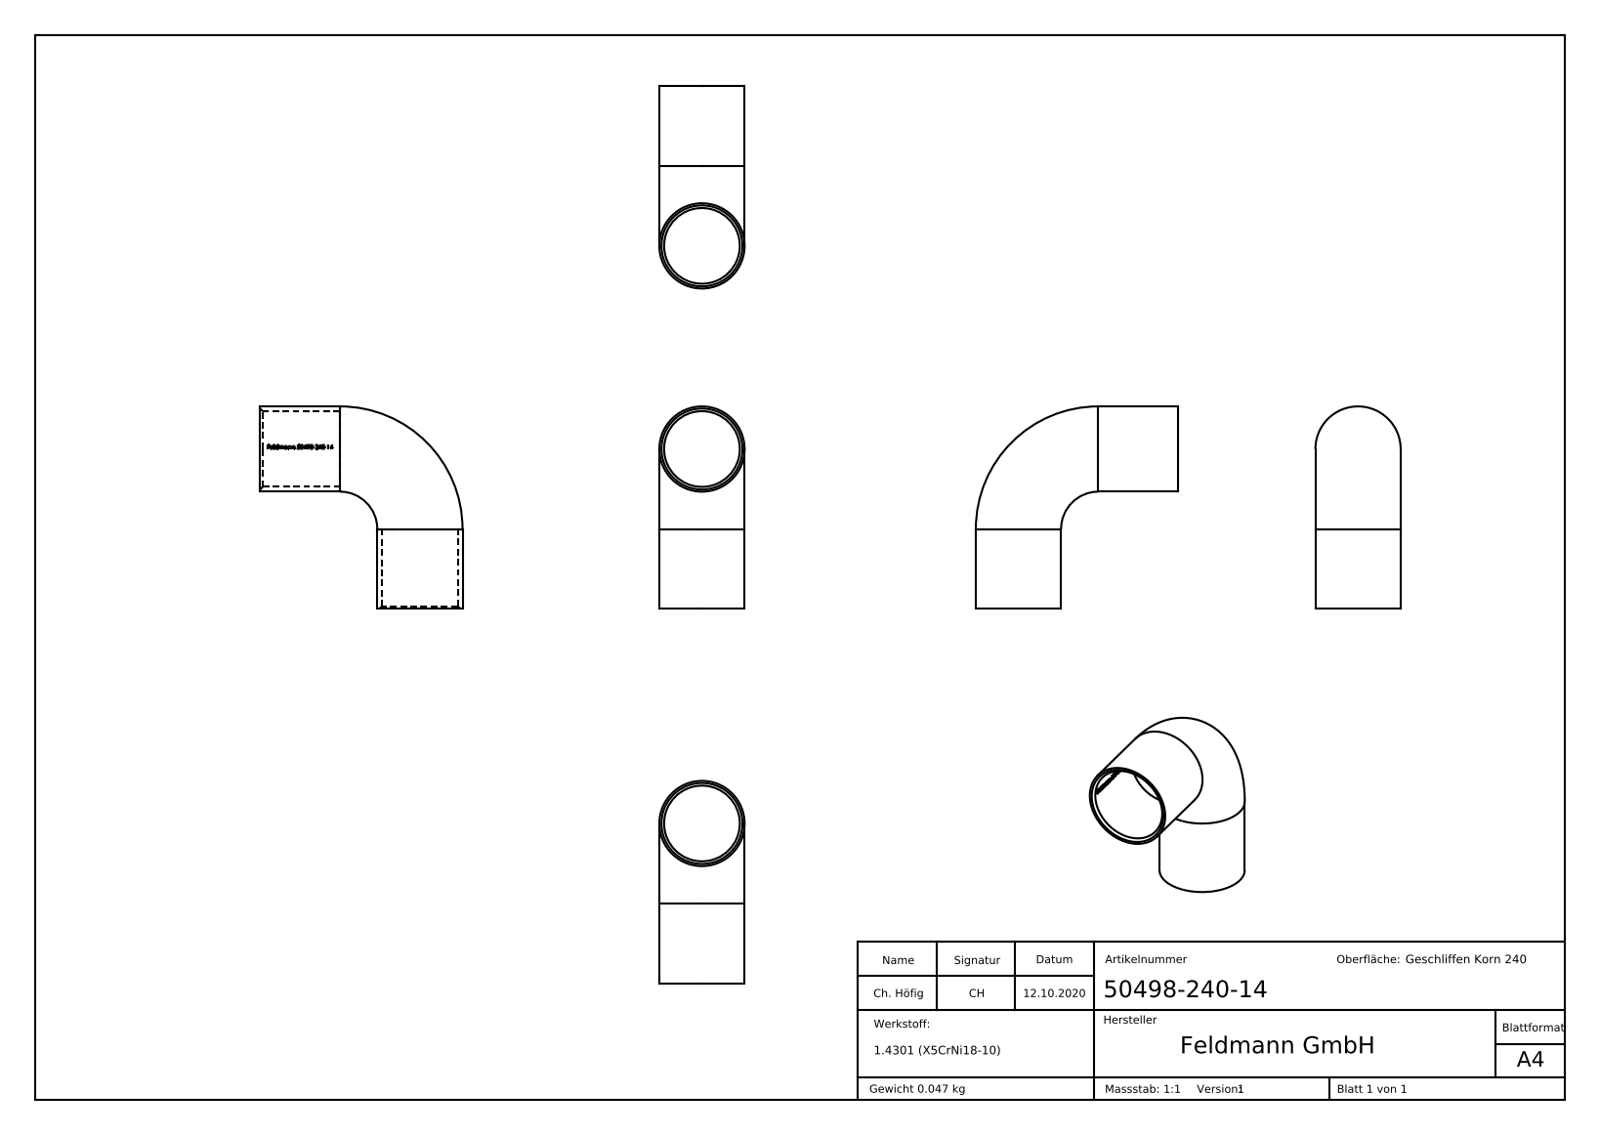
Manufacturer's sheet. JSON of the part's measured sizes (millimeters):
{"part_name": "50498-240-14", "step_written_by": "SolidWorks 2018 (CONFIG_CONTROL_DESIGN)", "units": "millimeters", "bodies": {"solids": 1, "faces": 277, "planar": 126, "cylindrical": 39, "other": 112}, "overall_size": [38, 38, 16], "volume_mm3": 6007, "surface_area_mm2": 4414, "round_holes": [[14.2, 2]], "round_bosses_or_shafts": [[16, 2]], "partial_cylinders_radius": [[7.2, 1]], "face_to_face_distances": [15, 2.2, 11.44, 2.13, 1.46, 9.98, 30, 30.26, 15.26, 0.53]}
